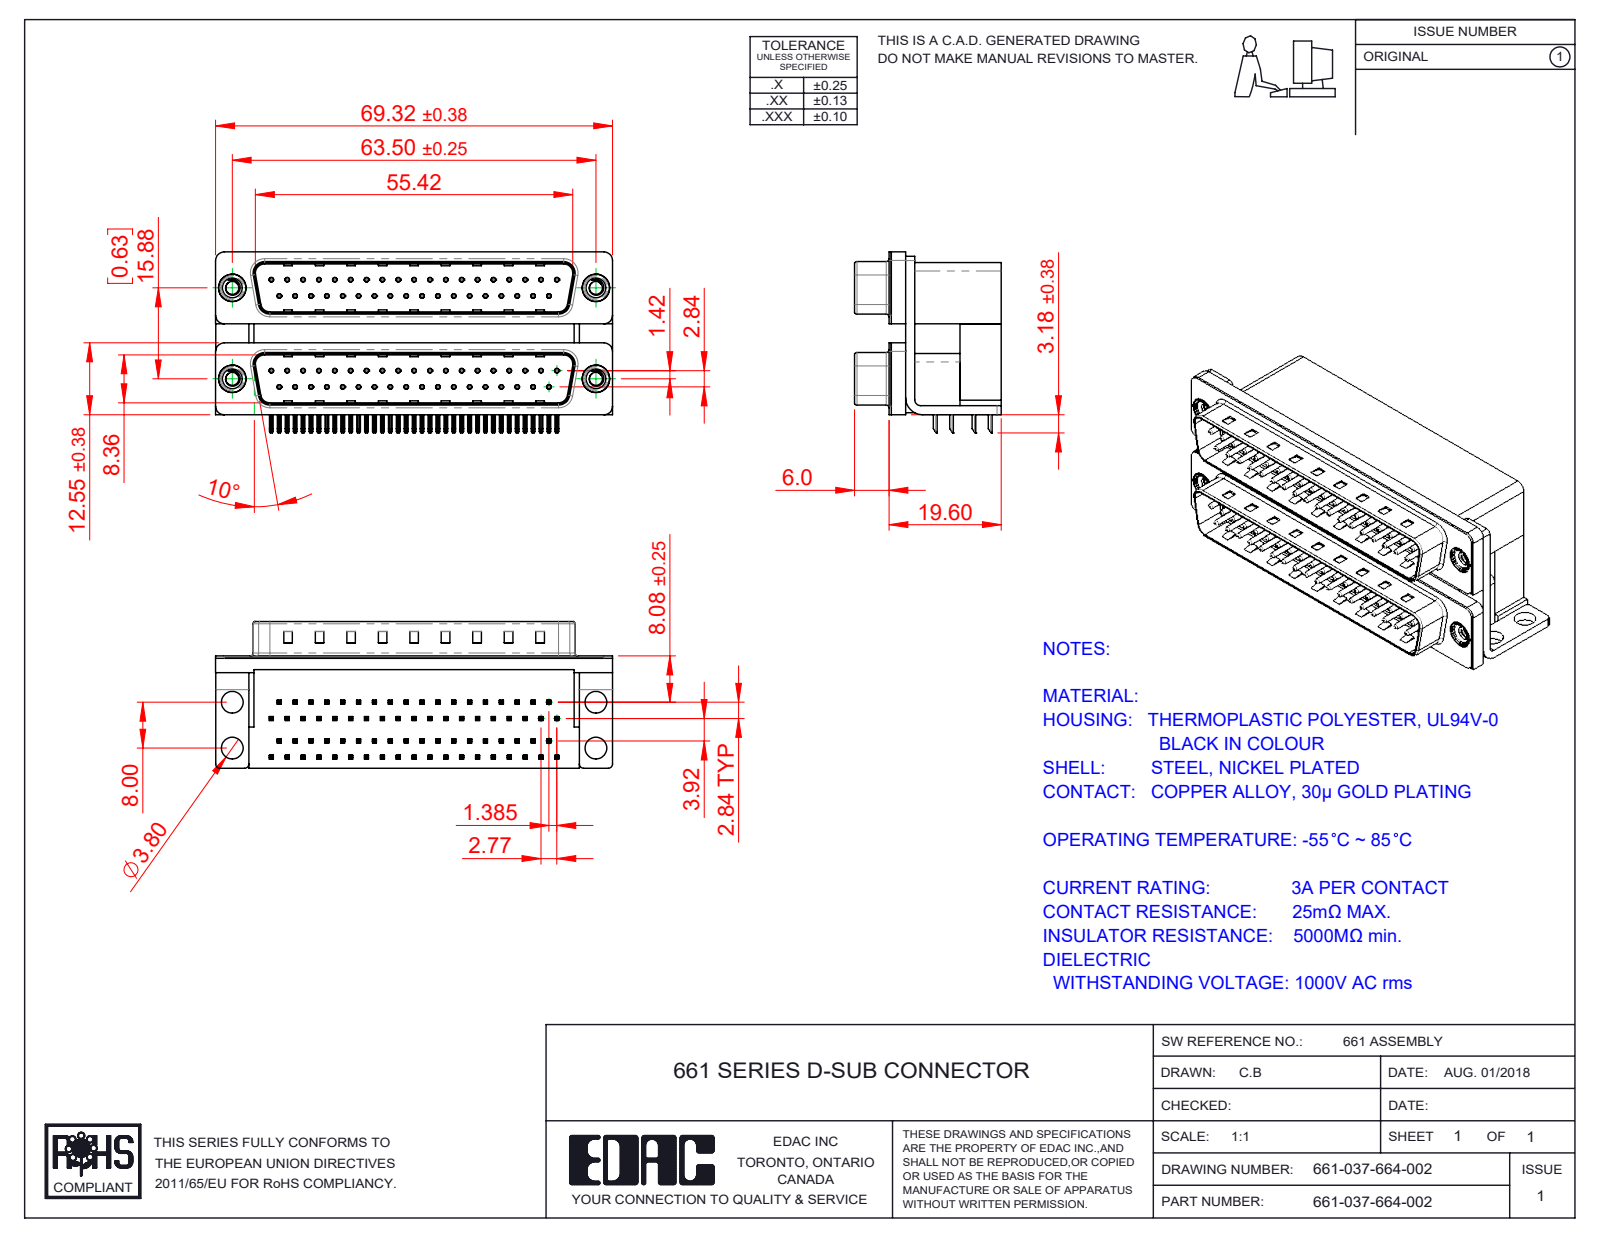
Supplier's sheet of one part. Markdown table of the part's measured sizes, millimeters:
| quantity | value |
| --- | --- |
| part name | 661 Mounting Bracket_NoneL; 661 Shell_37 Contacts; 661 Contact Top Upper_L; 661 Contact Top Lower (+7 more) |
| STEP written by | SolidWorks 2020 (CONFIG_CONTROL_DESIGN) |
| units | millimeters |
| bodies | 85 solids, 6582 faces (4250 planar, 1794 cylindrical, 538 other) |
| overall size | 69.32 × 31.61 × 25.6 |
| volume | 27 918 mm³ |
| surface area | 28 516 mm² |
| round holes (diameter × count) | 0.35 × 74, 0.8 × 74, 2.26 × 4, 3.5 × 4, 3.8 × 4, 4 × 4, 4.8 × 4, 5 × 4 |
| round bosses / shafts (diameter × count) | 0.75 × 74, 4.9 × 4, 4.75 × 4, 3.9 × 4 |
| partial cylindrical surfaces (radius × count) | 0.25 × 296, 0.12 × 148, 0.5 × 16, 1.5 × 13, 0.75 × 8, 0.9 × 8, 1.6 × 8, 2 × 8 |
| main face-to-face distances | 0.4, 19.2, 15.87, 7.2, 12, 10.7, 8.76, 15.52, 26.22, 2.19 |
| hole center spacings | 2.77, 5.54, 3.16, 8.31, 11.08, 13.85, 16.62, 19.39 |
